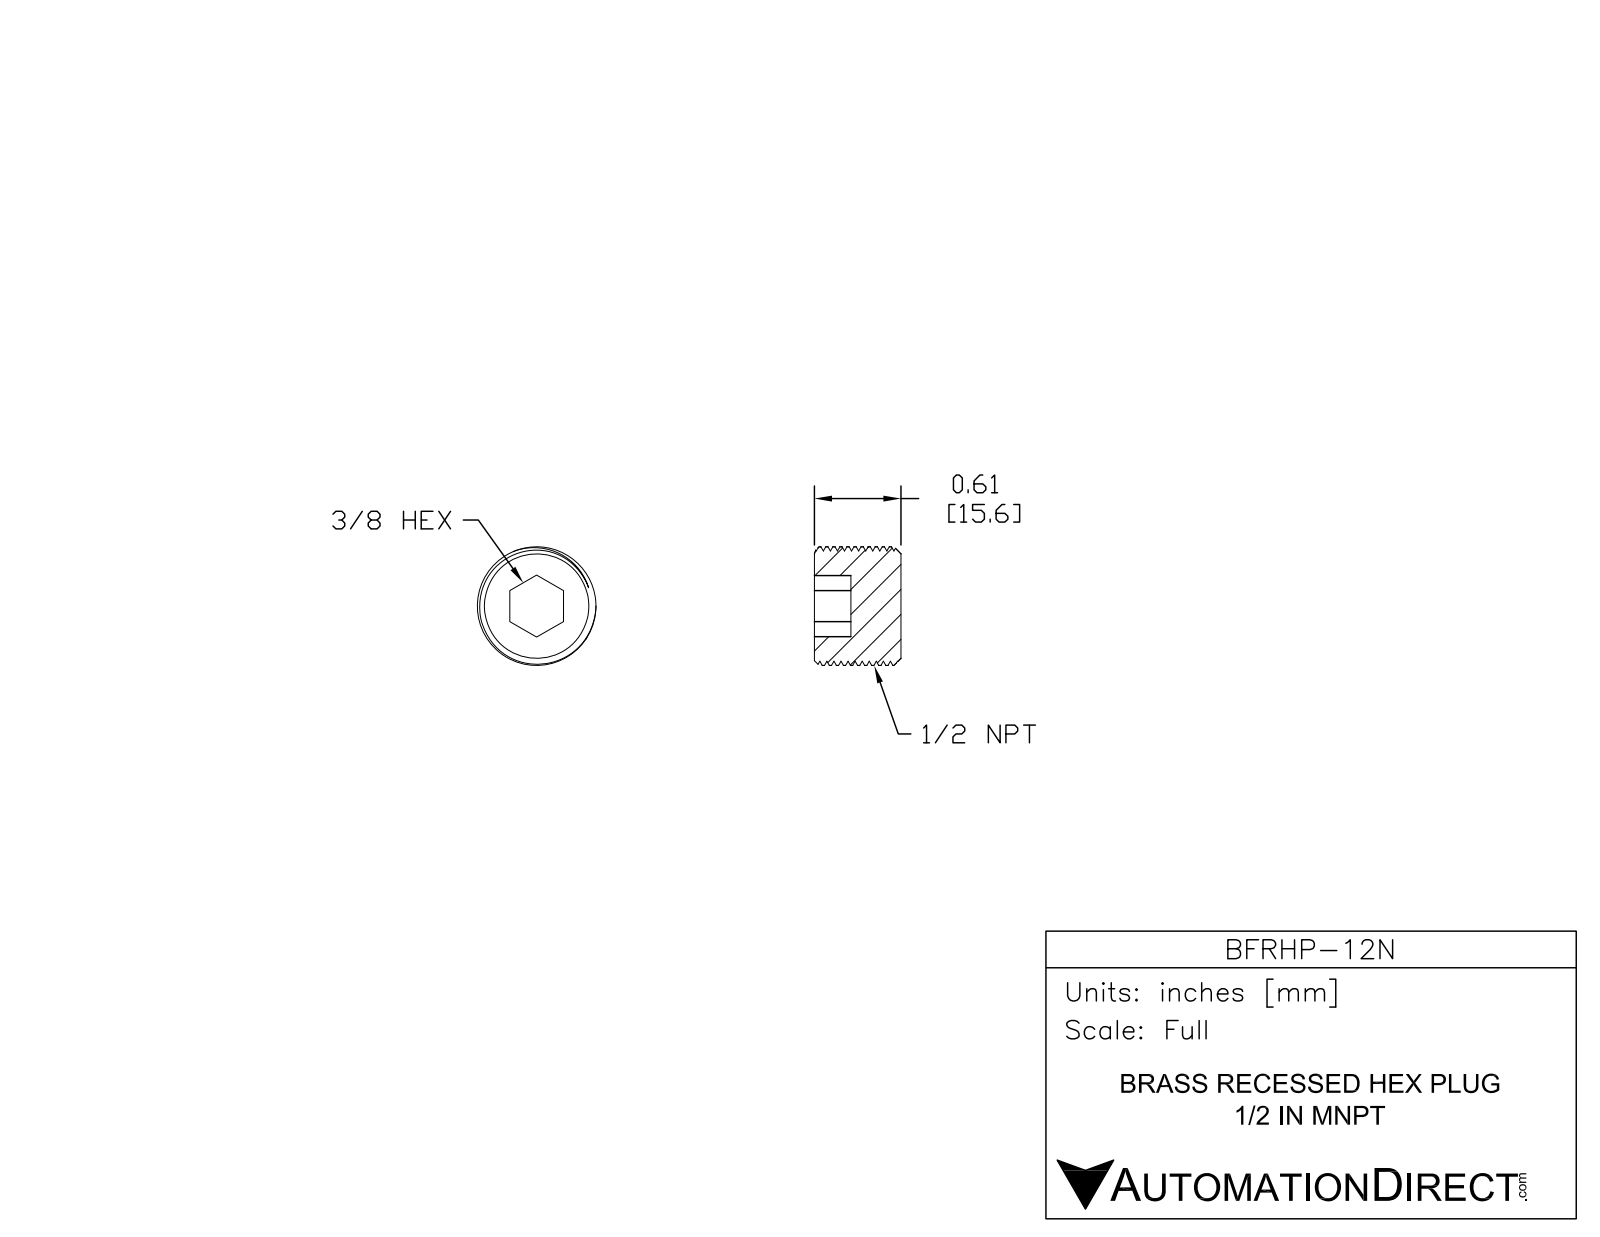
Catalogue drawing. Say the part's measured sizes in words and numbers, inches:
The part is named "BFRHP-12". Its 3-D file was written by "SolidWorks 2015 (CONFIG_CONTROL_DESIGN)". It is 1 solid with 37 faces: 9 planar, 22 cylindrical and 6 other. Overall it measures 0.84 by 0.84 by 0.63 inches. Its volume is 0.295 cubic inches and its surface area 3.881 square inches. Round bosses or shafts: 1 of diameter 0.84. The main face-to-face distances are 0.63, 0.355, 0.275.
